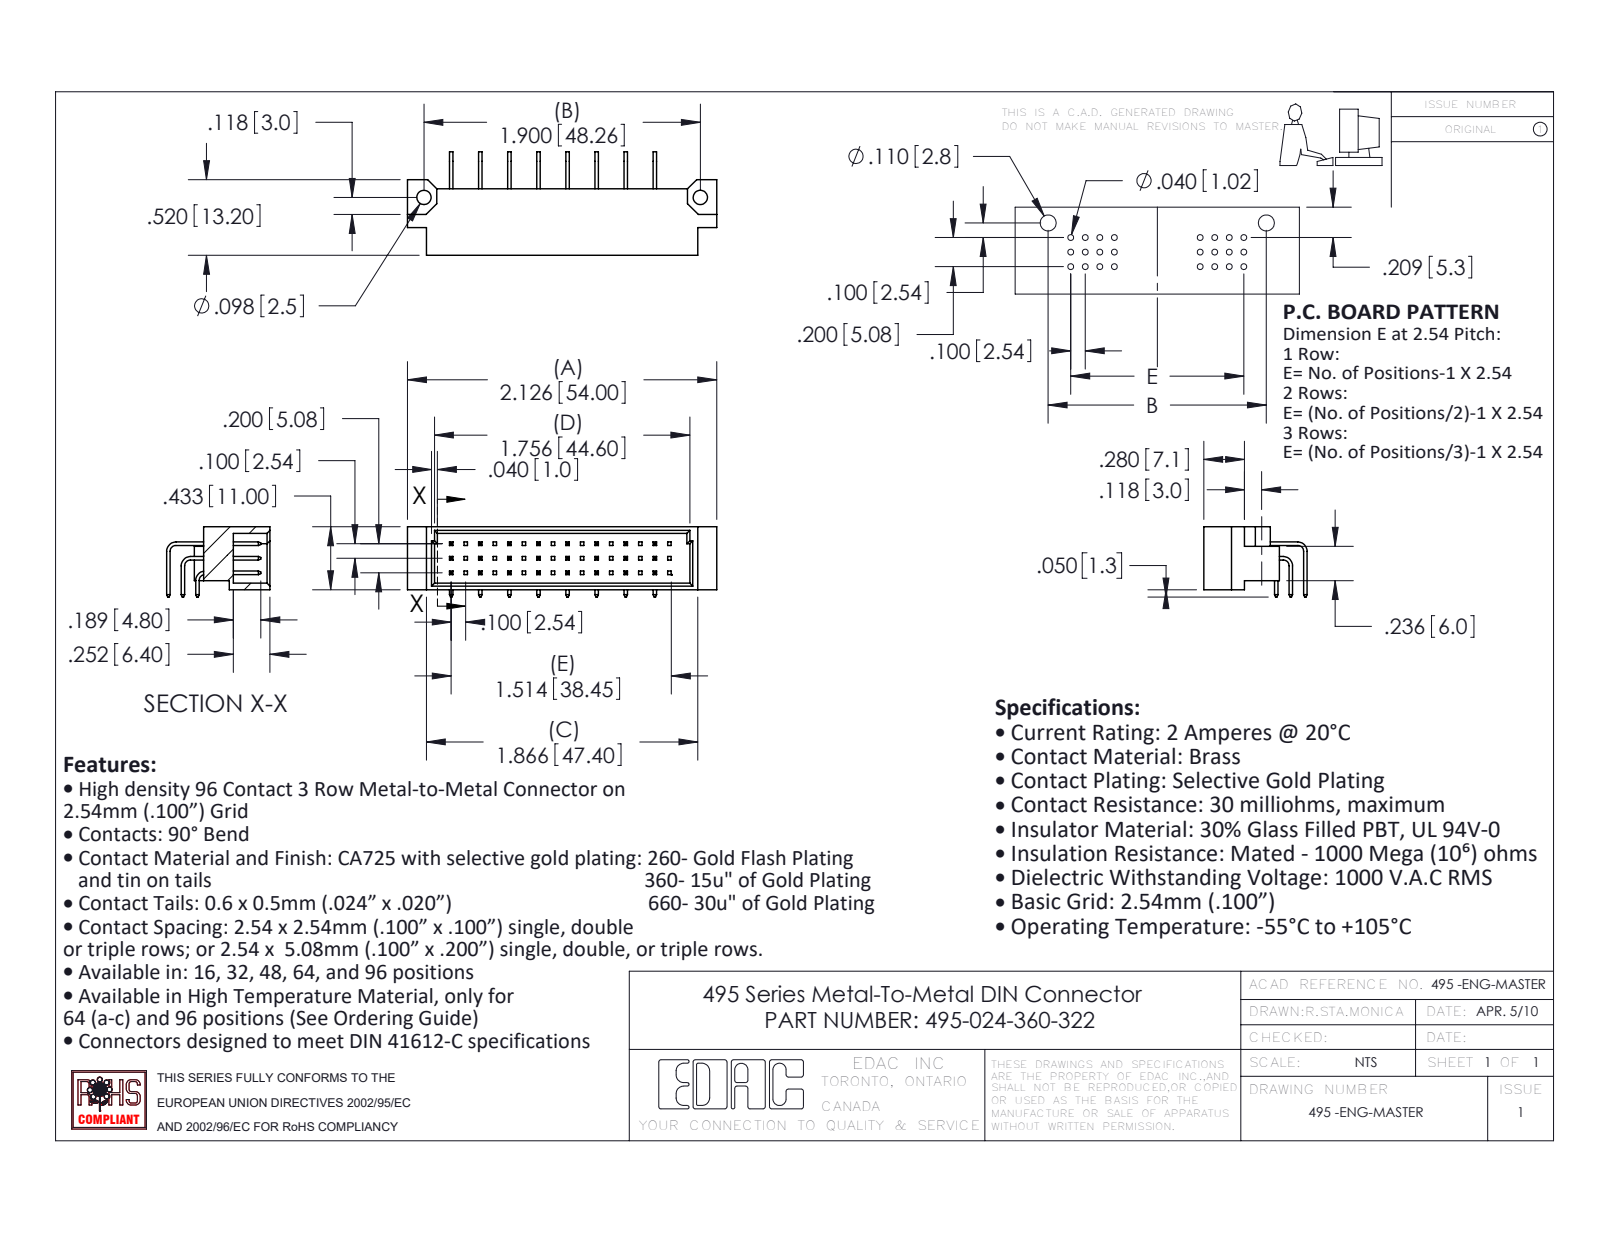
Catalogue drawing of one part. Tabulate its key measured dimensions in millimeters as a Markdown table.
| quantity | value |
| --- | --- |
| part name | 495-290-1; 495 Part_48; 495-290-2; 495-024-360-322 (+1 more) |
| STEP written by | SolidWorks 2020 (AUTOMOTIVE_DESIGN) |
| units | millimeters |
| bodies | 25 solids, 674 faces (622 planar, 52 cylindrical, 0 other) |
| overall size | 54 × 18.05 × 12.27 |
| volume | 3 622 mm³ |
| surface area | 5 113 mm² |
| round holes (diameter × count) | 2.49 × 2 |
| partial cylindrical surfaces (radius × count) | 1.02 × 3, 1.65 × 3 |
| main face-to-face distances | 5.08, 10.16, 1.14, 9.86, 2.54, 5.2, 15.24, 0.61, 0.6, 20.32 |
| hole center spacings | 48.26 |
